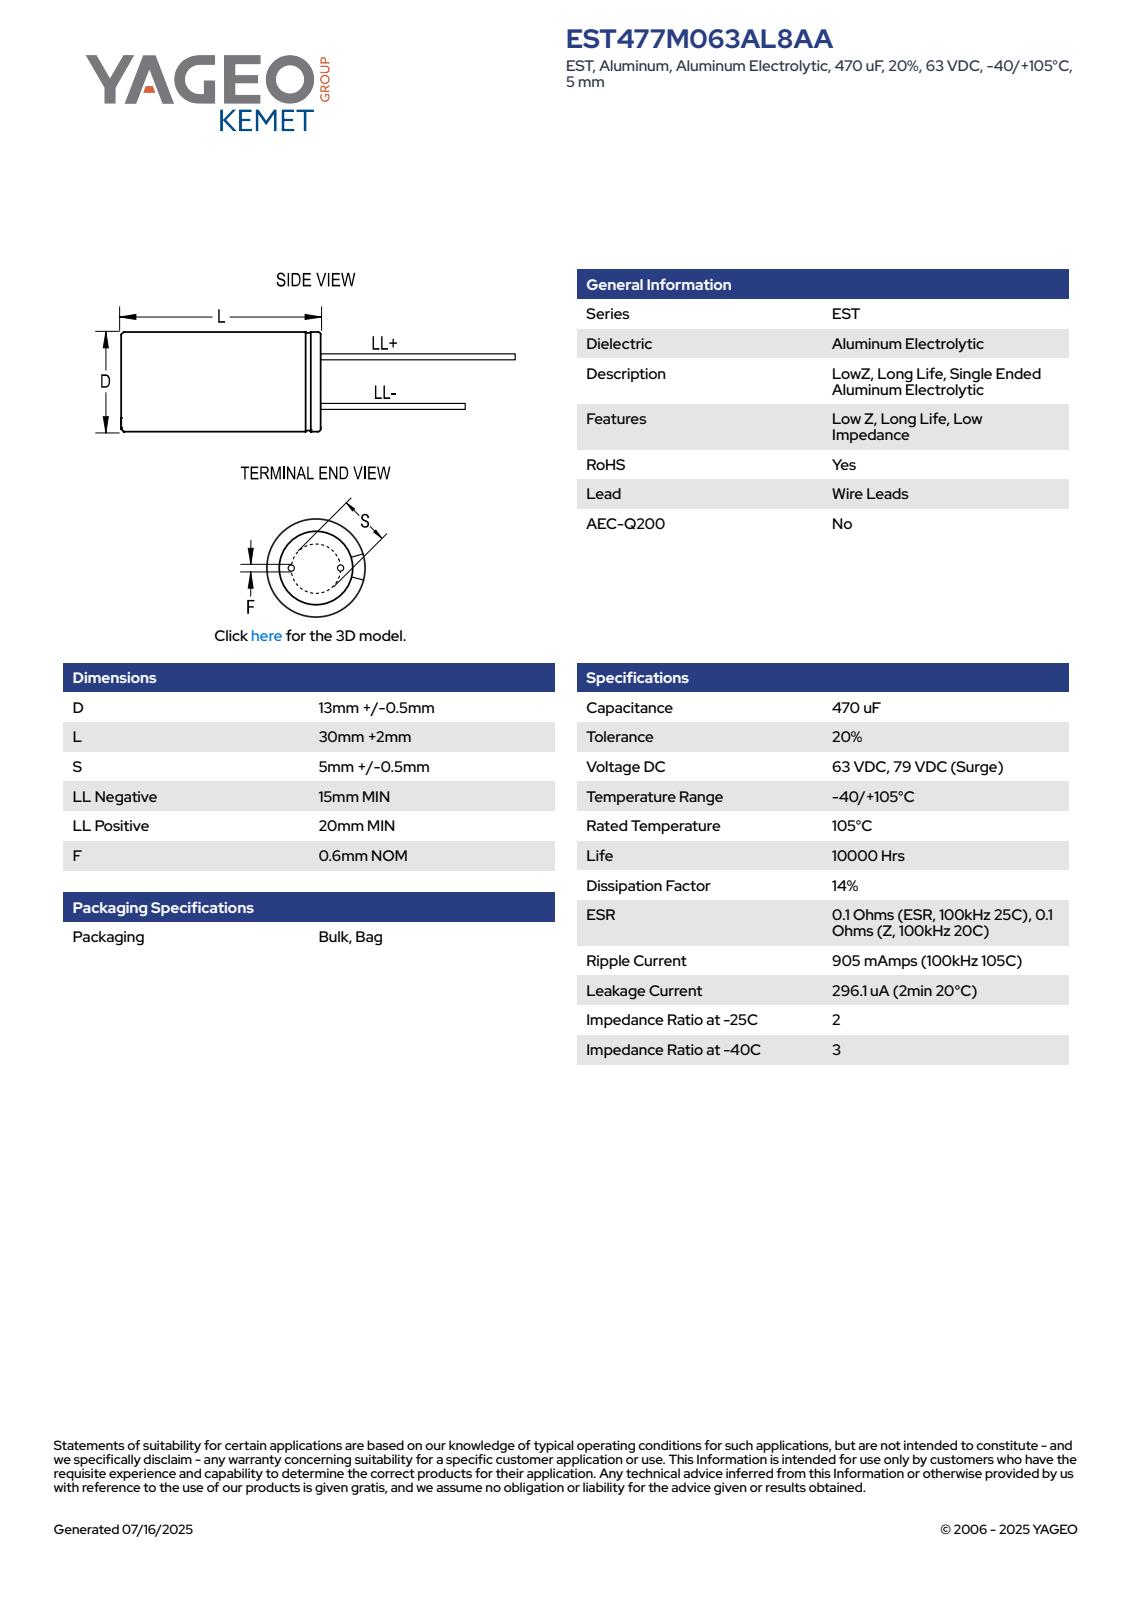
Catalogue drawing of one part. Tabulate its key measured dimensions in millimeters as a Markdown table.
| quantity | value |
| --- | --- |
| part name | CAR_KLP_13X30_D13.5L32S5F0.6 |
| STEP written by | SolidWorks 2014 (AUTOMOTIVE_DESIGN) |
| units | millimeters |
| bodies | 4 solids, 75 faces (61 planar, 8 cylindrical, 6 other) |
| overall size | 52.01 × 13.5 × 13.5 |
| volume | 4 565 mm³ |
| surface area | 1 751 mm² |
| round bosses / shafts (diameter × count) | 0.6 × 2, 13.5 × 1 |
| main face-to-face distances | 32, 32.01, 47.01, 52.01, 47, 52, 15, 20, 5, 1.81 |
